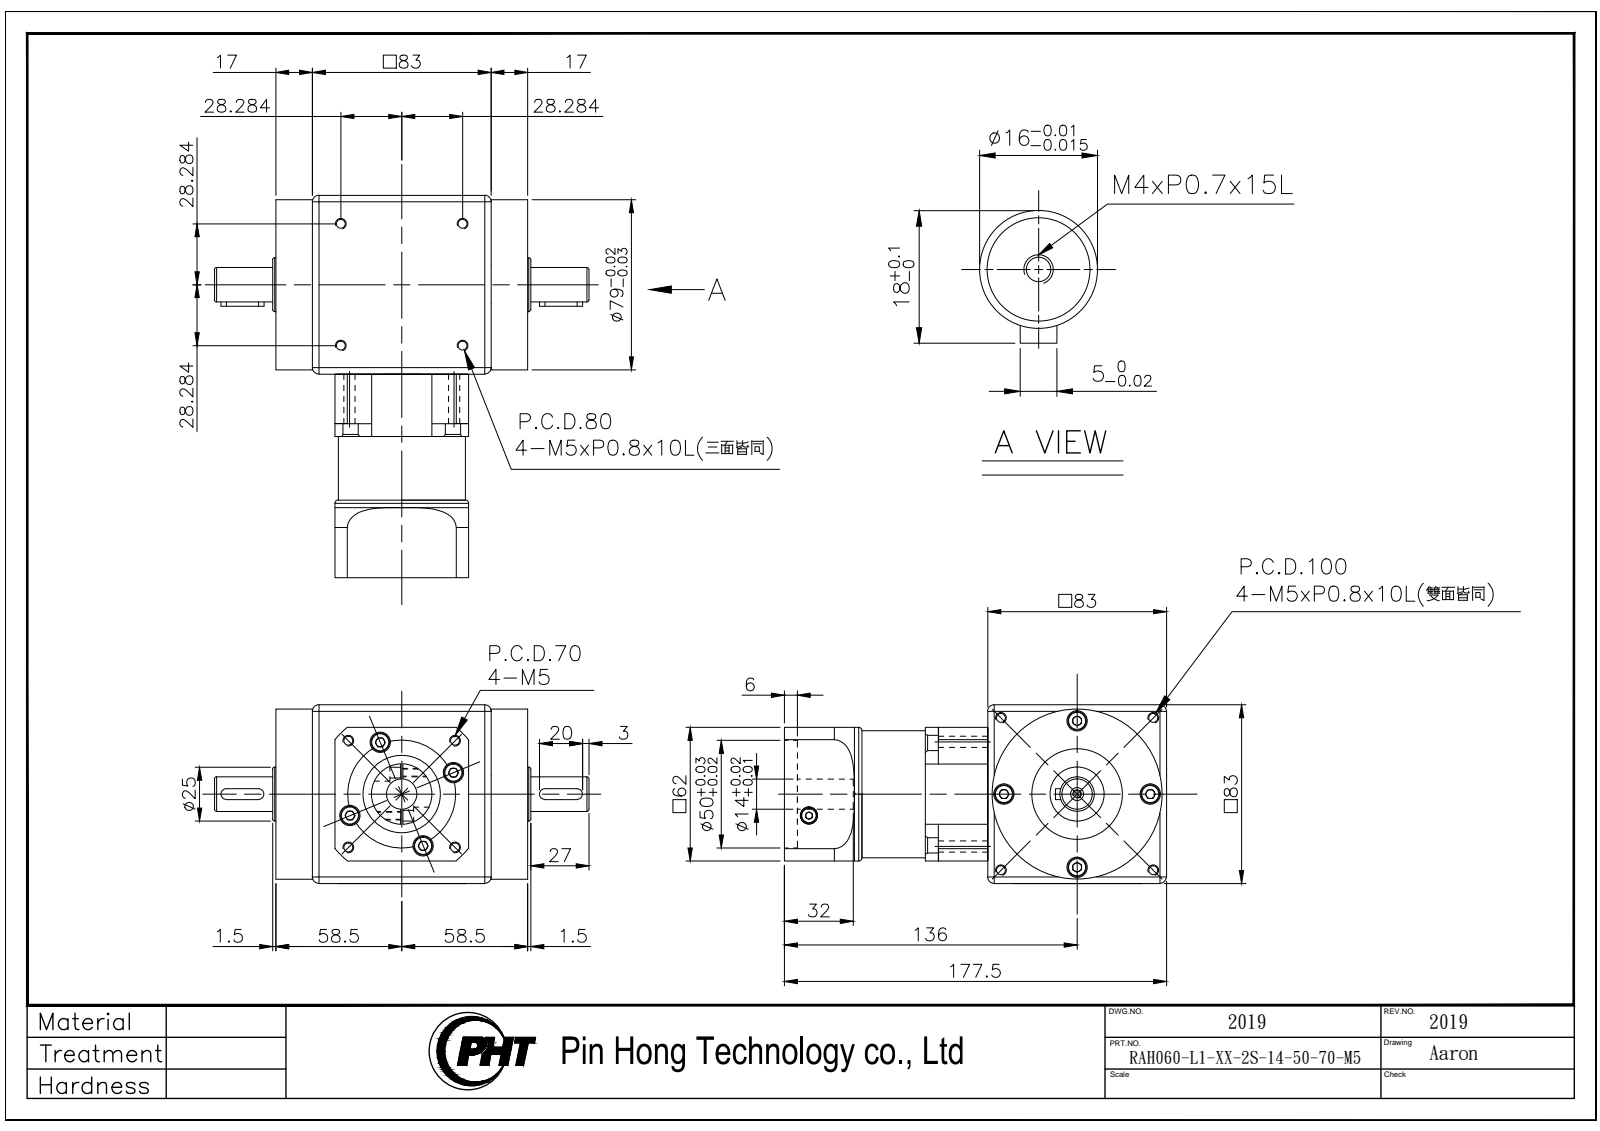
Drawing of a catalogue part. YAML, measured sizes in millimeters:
part_name: "RAH060-L1-XX-2S-14-50-70-M5_2019"
step_written_by: "SolidWorks 2016 (AUTOMOTIVE_DESIGN)"
units: millimeters
bodies: {solids: 3, faces: 609, planar: 266, cylindrical: 215, other: 128}
overall_size: [177.5, 174, 83]
volume: 1027000
surface_area: 106520
round_holes:
  - {diameter: 4.2, count: 16}
  - {diameter: 5.2, count: 8}
  - {diameter: 9.5, count: 8}
  - {diameter: 5.5, count: 4}
  - {diameter: 8, count: 2}
  - {diameter: 3.3, count: 1}
  - {diameter: 4, count: 1}
  - {diameter: 14, count: 1}
  - {diameter: 36, count: 1}
round_bosses_or_shafts:
  - {diameter: 8.5, count: 12}
  - {diameter: 79, count: 1}
  - {diameter: 61.8, count: 1}
  - {diameter: 59, count: 1}
  - {diameter: 55, count: 1}
  - {diameter: 42, count: 1}
  - {diameter: 28, count: 1}
  - {diameter: 25, count: 1}
partial_cylinders:
  - {radius: 2.5, count: 4}
  - {radius: 5, count: 4}
  - {radius: 25, count: 1}
  - {radius: 34, count: 1}
  - {radius: 40, count: 1}
  - {radius: 57.15, count: 1}
face_to_face_distances: [83, 10.5, 72.5, 89.5, 62, 27.5, 117, 17, 100, 2]
hole_center_spacings: [53.15, 56.56, 4.99, 14.82, 18.82, 26, 34.71, 35]
